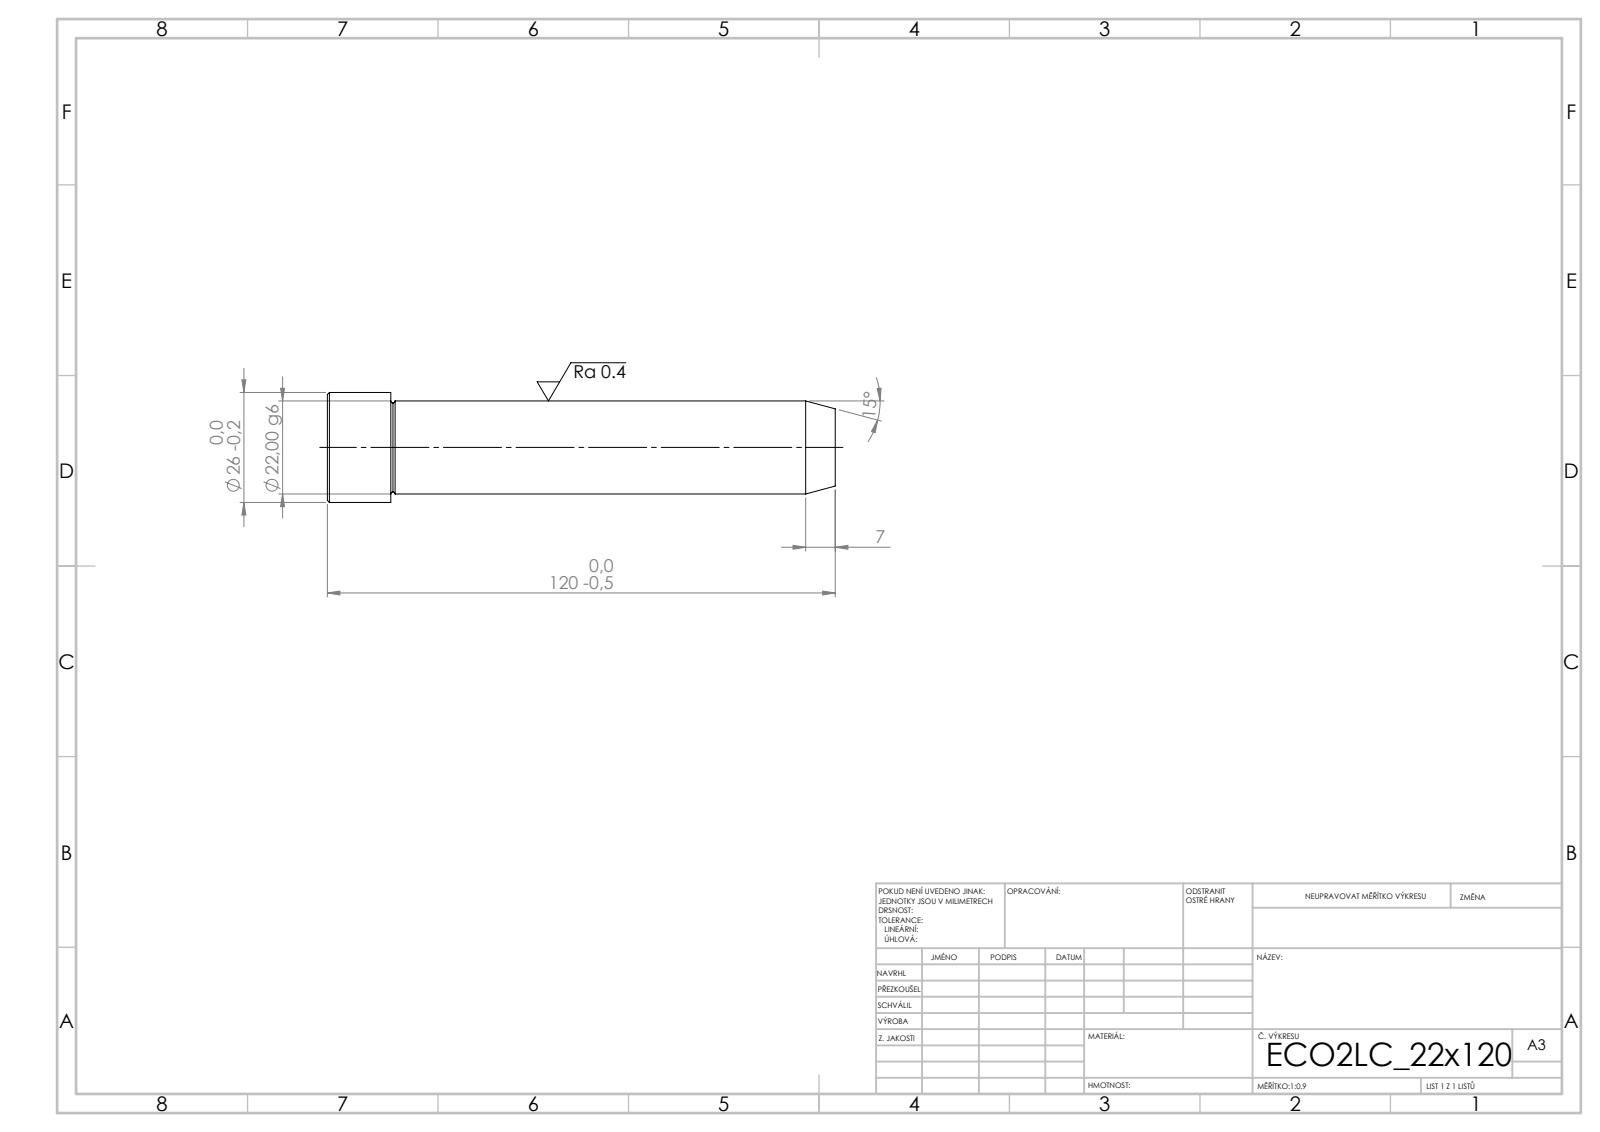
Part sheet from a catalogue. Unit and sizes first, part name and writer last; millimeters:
Units: millimetres
Overall size (bounding box): 120 × 26 × 26
Round bosses / shafts (diameter × count): ⌀26 ×1, ⌀22 ×1
Main face-to-face distances: 120, 105, 15
Volume: 47 413 mm³ · Surface area: 9 412 mm²
Bodies: 1 solid, 15 faces (3 planar, 4 cylindrical, 8 other)
STEP written by: SolidWorks 2019 (CONFIG_CONTROL_DESIGN)
